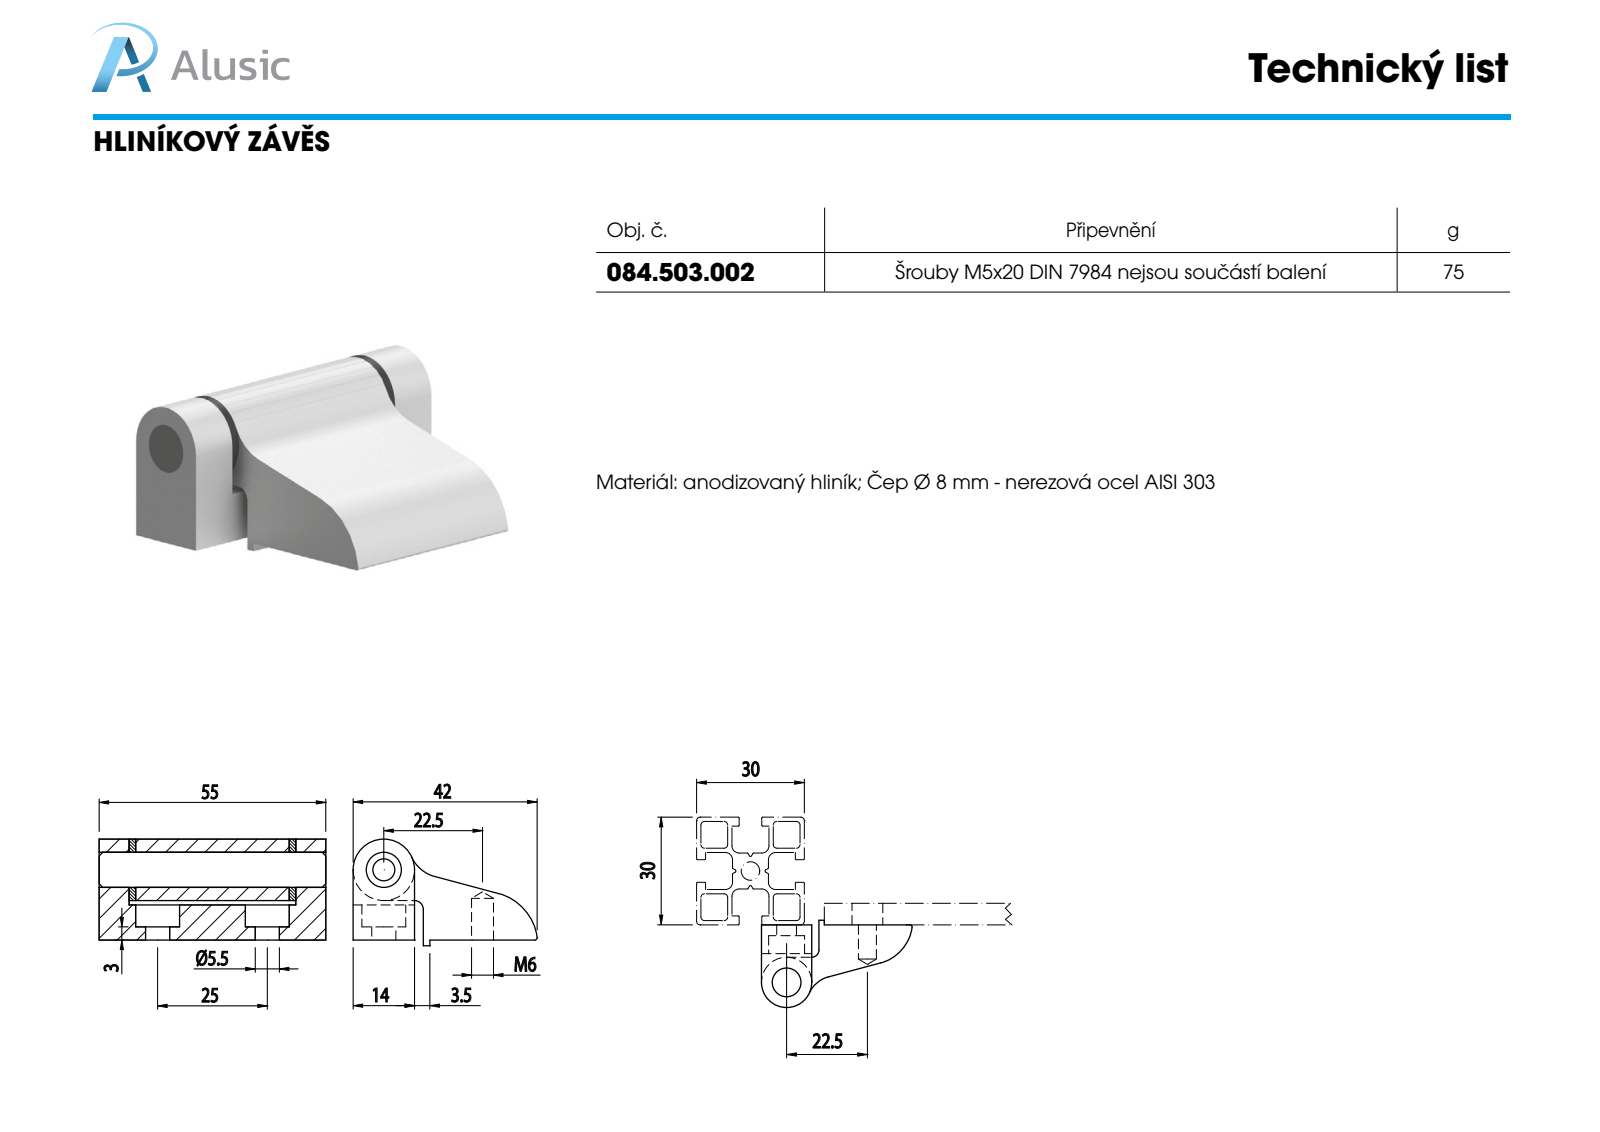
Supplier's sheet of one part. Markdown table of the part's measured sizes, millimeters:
| quantity | value |
| --- | --- |
| part name | 084.503.002; CERNIERA MOBILE MACAP PICCOLA; CERNIERA FISSA MACAP PICCOLA; BOCCOLA |
| STEP written by | SolidWorks 2012 (CONFIG_CONTROL_DESIGN) |
| units | millimeters |
| bodies | 4 solids, 56 faces (22 planar, 32 cylindrical, 2 other) |
| overall size | 55 × 41.94 × 24.3 |
| volume | 22 538 mm³ |
| surface area | 10 878 mm² |
| round holes (diameter × count) | 5 × 2, 5.5 × 2, 10 × 2, 8 × 1 |
| round bosses / shafts (diameter × count) | 14 × 1 |
| partial cylindrical surfaces (radius × count) | 0.5 × 1, 2 × 1, 8 × 1, 12 × 1 |
| main face-to-face distances | 1.5, 14, 35, 36.5, 8.5, 10, 45, 46.5, 8, 16 |
| hole center spacings | 25.74, 25 |
